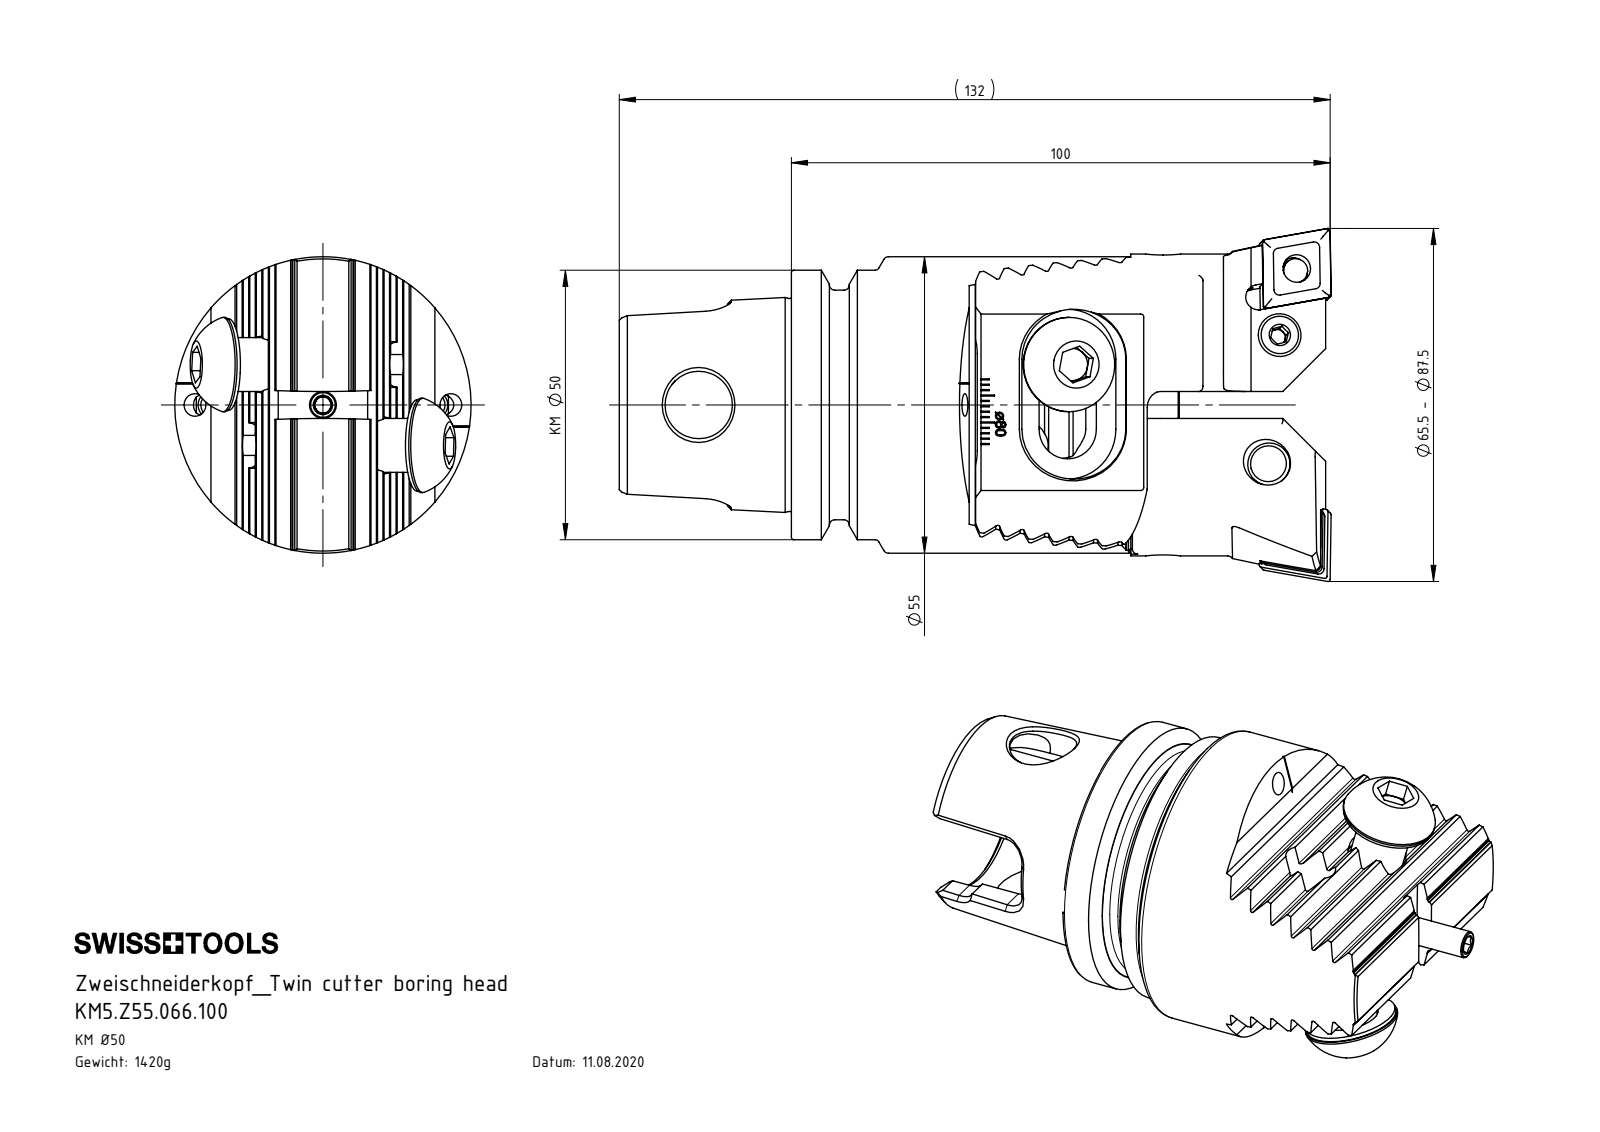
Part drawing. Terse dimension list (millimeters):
name: Z55-ER1.003.025_A_gespannt; Z55-ER1.002.025_A; KM5.Z55.K23.100; KM5-Z55.K23.100_C (+2 more)
written by: SolidWorks 2017 (AUTOMOTIVE_DESIGN)
unit: mm
bodies: 6 solids, 304 faces (168 planar, 72 cylindrical, 64 other)
size: 103.95 × 55 × 55
volume: 116 474 mm³; area: 27 794 mm²
holes: 3× ⌀4.2, 3× ⌀8.5, 2× ⌀10.5, 2× ⌀11, 1× ⌀3, 1× ⌀3.3, 1× ⌀12.5, 1× ⌀24.5, 1× ⌀28.27, 1× ⌀30
bosses: 2× ⌀17.5, 2× ⌀17, 2× ⌀10, 1× ⌀55, 1× ⌀50, 1× ⌀42.6, 1× ⌀5, 1× ⌀4
rounds: 14× R0.34, 3× R4, 2× R6.04, 2× R220
face distances: 4.07, 8.14, 12.21, 16.28, 20.35, 6.6, 63, 33, 30, 0.5
hole spacings: 41.2
